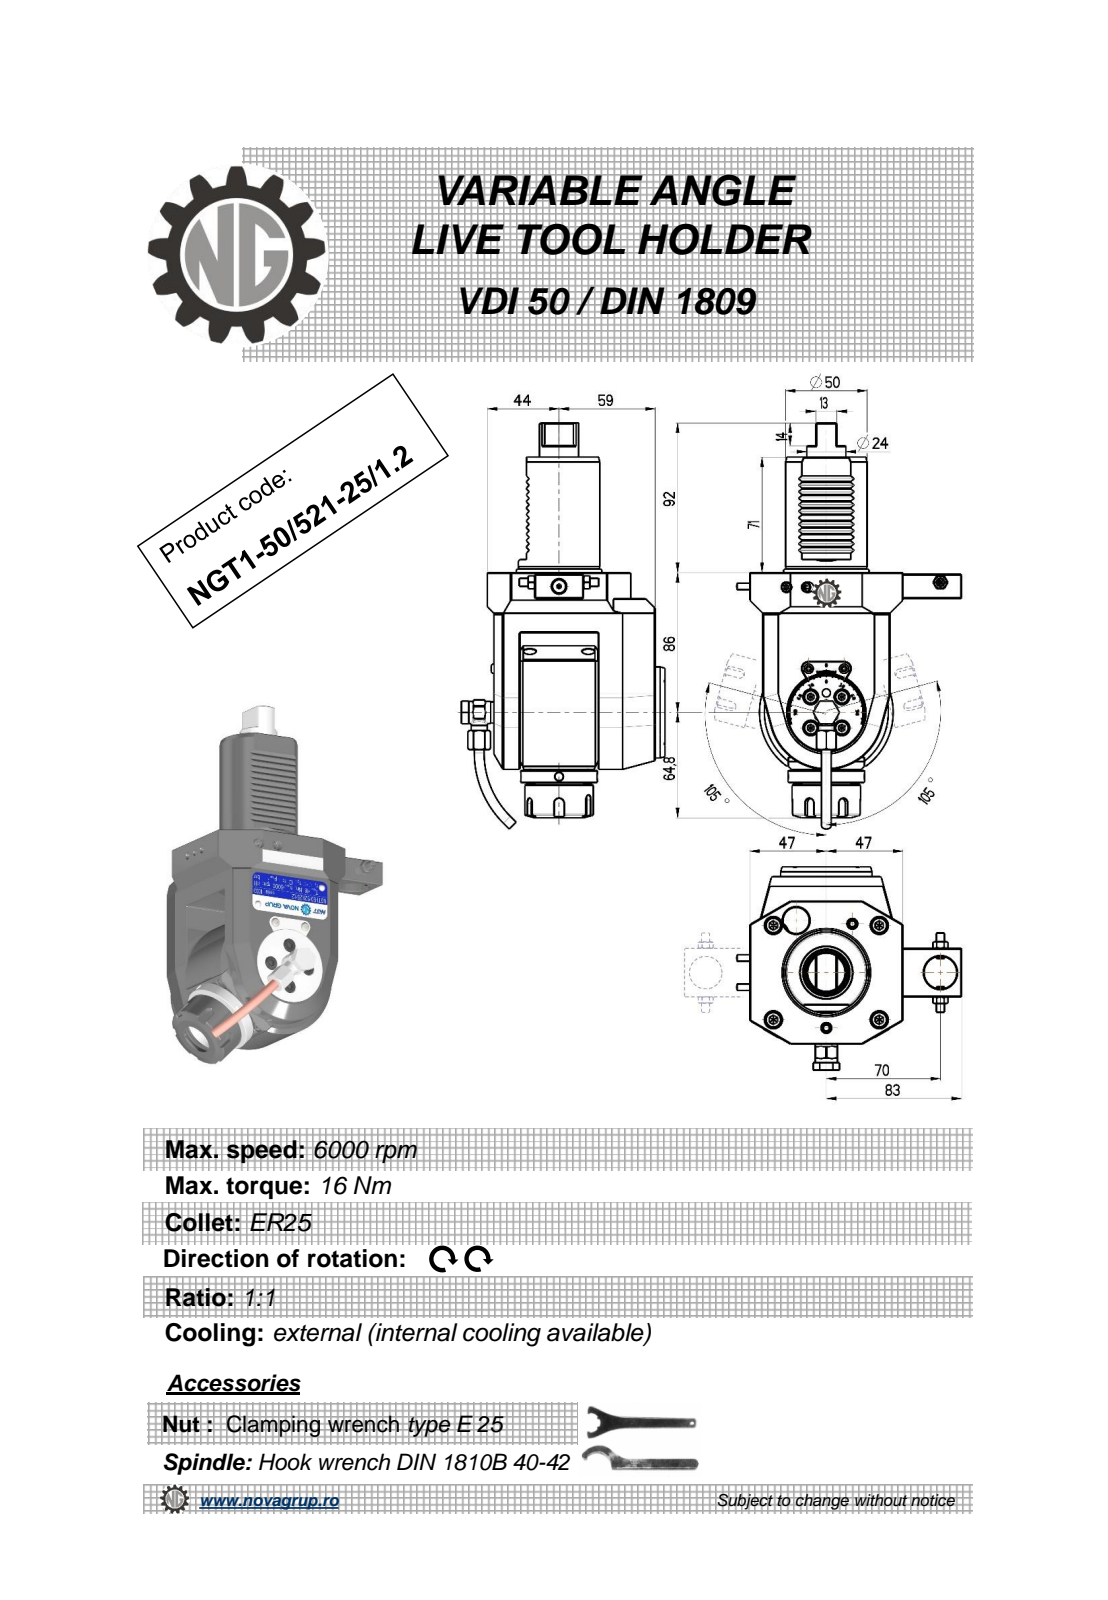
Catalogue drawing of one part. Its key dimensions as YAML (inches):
part_name: "NGT1_50_521_25_1_2"
step_written_by: "PRO/ENGINEER BY PARAMETRIC TECHNOLOGY CORPORATION, 2010280 (CONFIG_CONTROL_DESIGN)"
units: inches
bodies: {solids: 1, faces: 596, planar: 265, cylindrical: 138, other: 193}
overall_size: [9.83, 5.118, 4.917]
volume: 61.94
surface_area: 141.7
round_holes:
  - {diameter: 0.157, count: 3}
  - {diameter: 0.197, count: 2}
  - {diameter: 0.118, count: 1}
  - {diameter: 0.244, count: 1}
  - {diameter: 0.354, count: 1}
  - {diameter: 0.374, count: 1}
  - {diameter: 0.394, count: 1}
  - {diameter: 0.433, count: 1}
  - {diameter: 0.787, count: 1}
  - {diameter: 0.799, count: 1}
round_bosses_or_shafts:
  - {diameter: 0.236, count: 2}
  - {diameter: 0.224, count: 2}
  - {diameter: 3.228, count: 1}
  - {diameter: 2.205, count: 1}
  - {diameter: 1.969, count: 1}
  - {diameter: 1.85, count: 1}
  - {diameter: 1.654, count: 1}
  - {diameter: 1.378, count: 1}
partial_cylinders:
  - {radius: 0.01, count: 12}
  - {radius: 0.012, count: 12}
  - {radius: 0.006, count: 6}
  - {radius: 0.118, count: 5}
  - {radius: 0.02, count: 4}
  - {radius: 0.031, count: 2}
  - {radius: 0.039, count: 2}
  - {radius: 0.394, count: 2}
face_to_face_distances: [1.457, 0.63, 3.898, 0.827, 0.315, 0.236, 2.52, 4.134, 0.787, 1.378]
hole_center_spacings: [0.016, 1.553, 1.929, 1.945, 2.756, 3.364, 3.373, 4.604]
